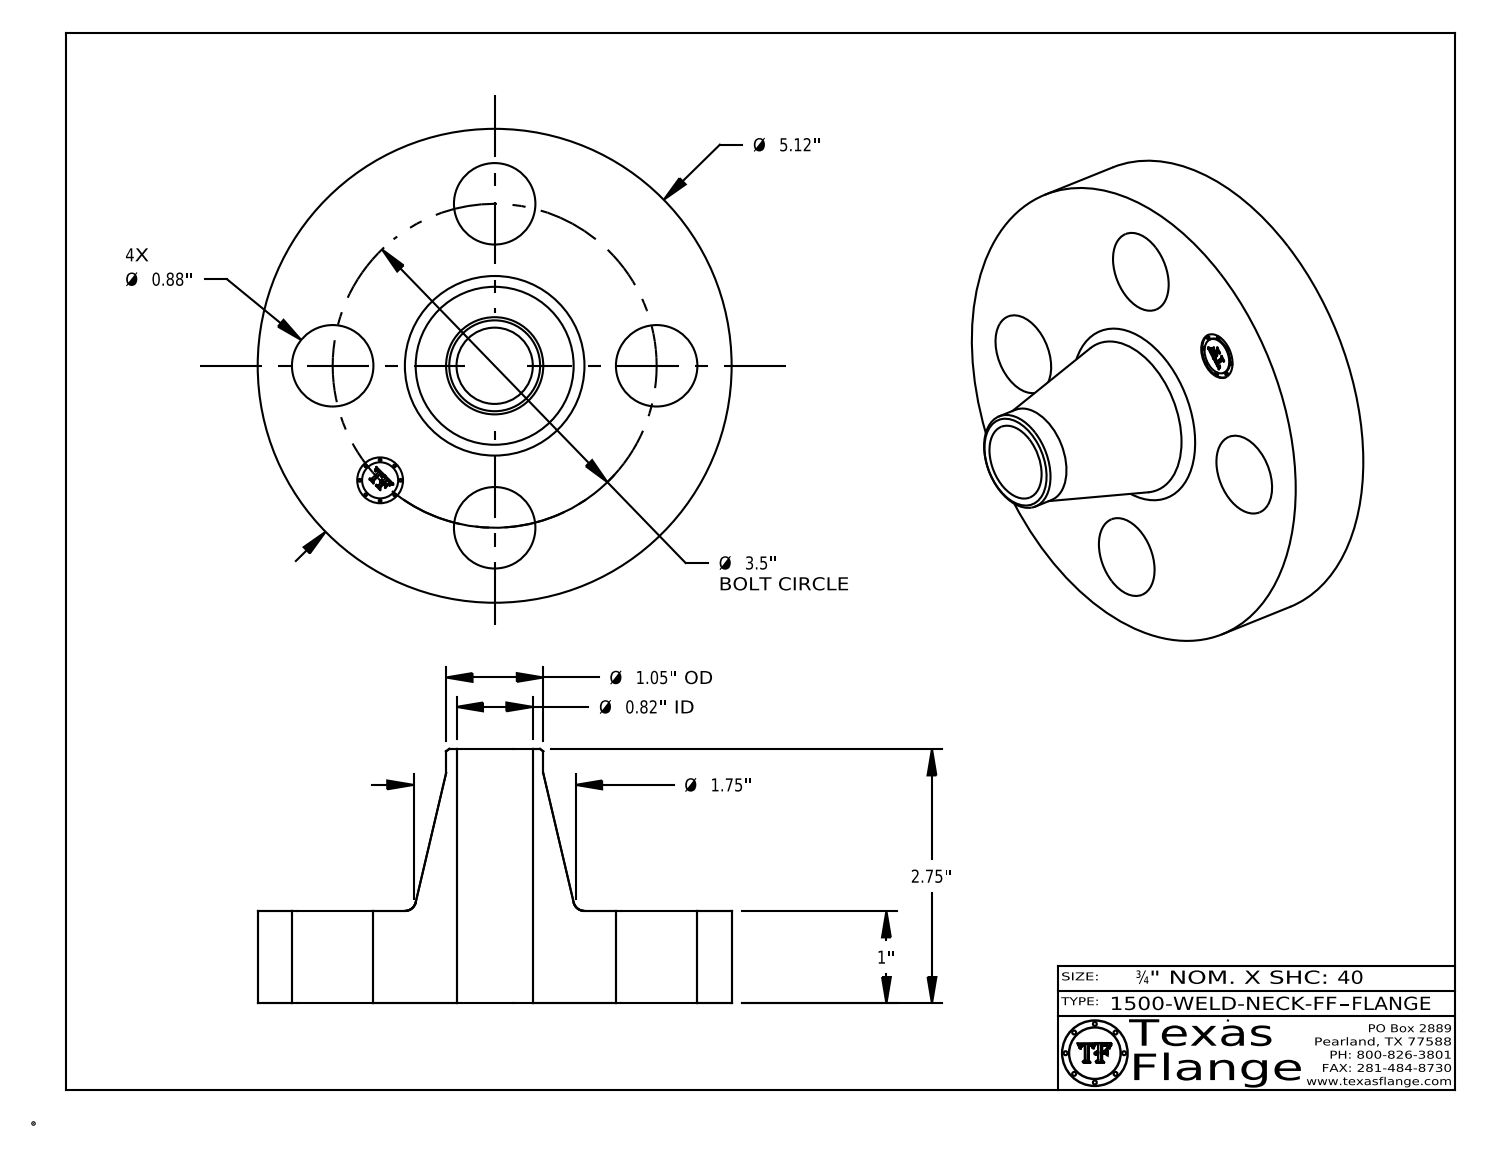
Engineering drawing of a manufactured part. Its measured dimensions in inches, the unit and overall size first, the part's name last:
Units: inches
Overall size (bounding box): 5.12 × 5.12 × 2.75
Round holes (diameter × count): ⌀0.88 ×4, ⌀0.495 ×1, ⌀0.824 ×1
Round bosses / shafts (diameter × count): ⌀0.03 ×8, ⌀5.12 ×1, ⌀1.05 ×1, ⌀0.39 ×1
Main face-to-face distances: 1, 2.75, 1.75, 0.015, 0.985, 1.765, 0.148, 0.145, 0.027, 0.096
Hole centre spacings: 1.75, 2.475, 1.339, 3.233, 3.5
Volume: 19.26 in³ · Surface area: 75.43 in²
Bodies: 1 solid, 408 faces (368 planar, 34 cylindrical, 6 other)
Part name (STEP PRODUCT): 1500-WELD-NECK-FF
STEP written by: CATIA V5 STEP AP214 (AUTOMOTIVE_DESIGN)
